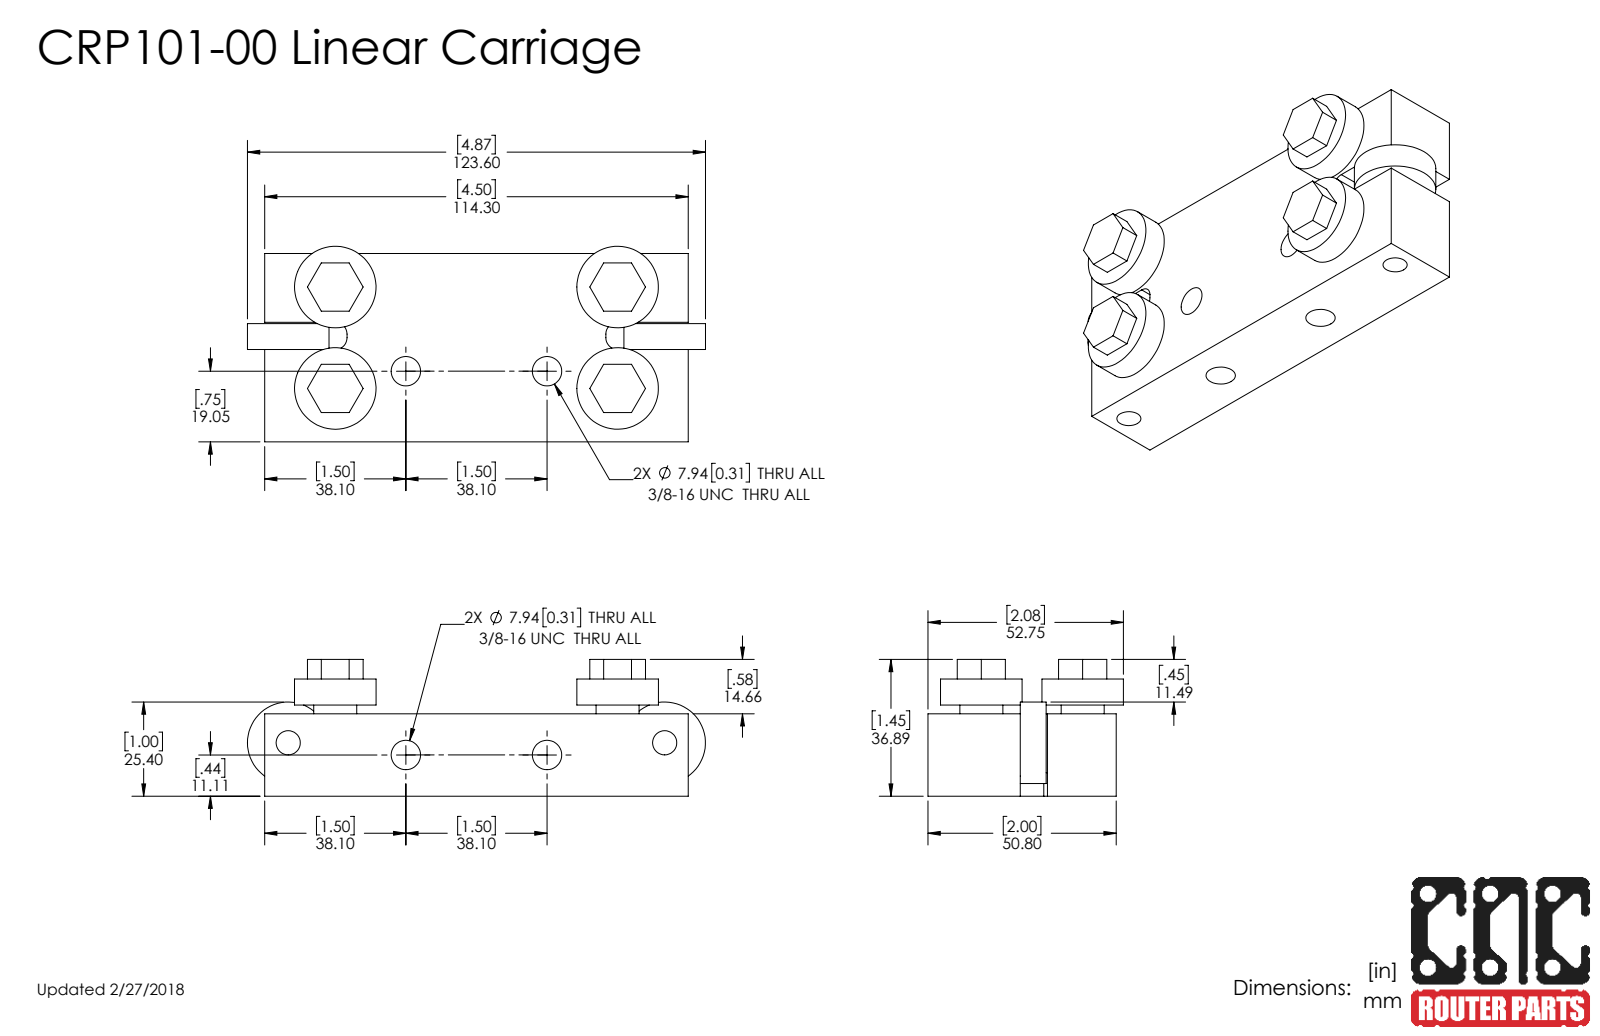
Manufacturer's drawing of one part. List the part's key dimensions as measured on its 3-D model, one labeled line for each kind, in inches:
Part name (STEP PRODUCT): HC-M8-20_91280A538; CRP101-00; 95610A180 M8 Washer; 0.3125in Jam Nut_93839A030 (+4 more)
STEP written by: SolidWorks 2017 (AUTOMOTIVE_DESIGN)
Units: inches
Bodies: 19 solids, 358 faces (126 planar, 134 cylindrical, 98 other)
Overall size (bounding box): 4.866 × 2.077 × 1.452
Volume: 7.804 in³ · Surface area: 64.22 in²
Round holes (diameter × count): ⌀0.313 ×6, ⌀0.315 ×6, ⌀0.268 ×4, ⌀0.313 ×4, ⌀0.201 ×2, ⌀0.257 ×2, ⌀0.268 ×2, ⌀0.316 ×2, ⌀0.375 ×2
Round bosses / shafts (diameter × count): ⌀0.866 ×6, ⌀0.457 ×4, ⌀0.25 ×2
Partial cylindrical surfaces — rounded edges, fillets, slot ends (radius × count): R0.125 ×4, R0.134 ×4, R0.157 ×2, R0.25 ×2
Main face-to-face distances: 0.875, 0.276, 2, 0.369, 1.243, 0.093, 0.968, 0.98, 1.02, 4.5
Hole centre spacings: 3, 0.511, 0.772, 0.787, 1.077, 1.167, 1.257, 1.5
